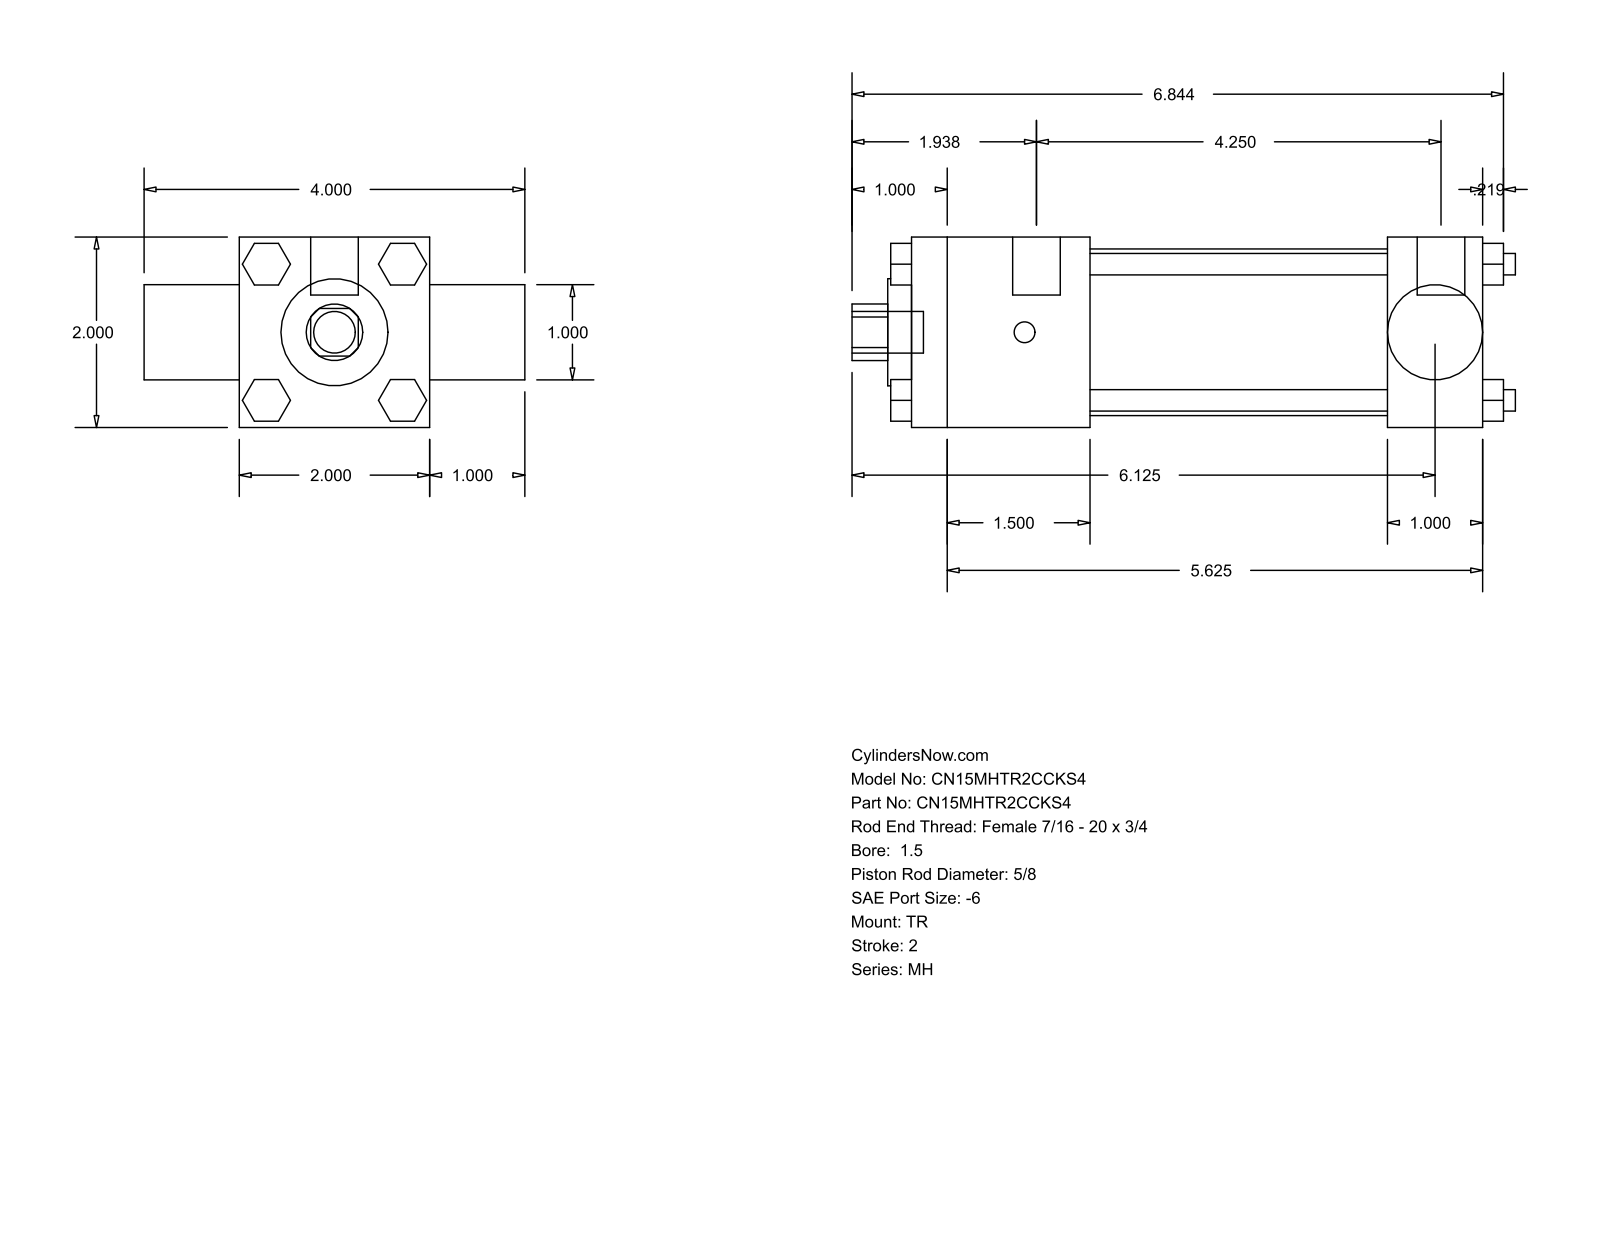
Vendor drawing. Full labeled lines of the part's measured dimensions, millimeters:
Part name (STEP PRODUCT): MH_TR__0150_0.625
STEP written by: GSSL Pune (CONFIG_CONTROL_DESIGN)
Units: millimetres
Bodies: 0 solids, 120 faces (92 planar, 28 cylindrical, 0 other)
Overall size (bounding box): 177.01 × 101.6 × 50.8
Round holes (diameter × count): ⌀15.88 ×1, ⌀25.35 ×1, ⌀28.57 ×1, ⌀44.45 ×1
Round bosses / shafts (diameter × count): ⌀5.71 ×4, ⌀5.56 ×3, ⌀12.7 ×2, ⌀11.11 ×1
Partial cylindrical surfaces — rounded edges, fillets, slot ends (radius × count): R7.54 ×1
Main face-to-face distances: 50.8, 25.4, 152.4, 76.2, 47.62, 104.78, 127, 79.38, 11.11, 18.16
